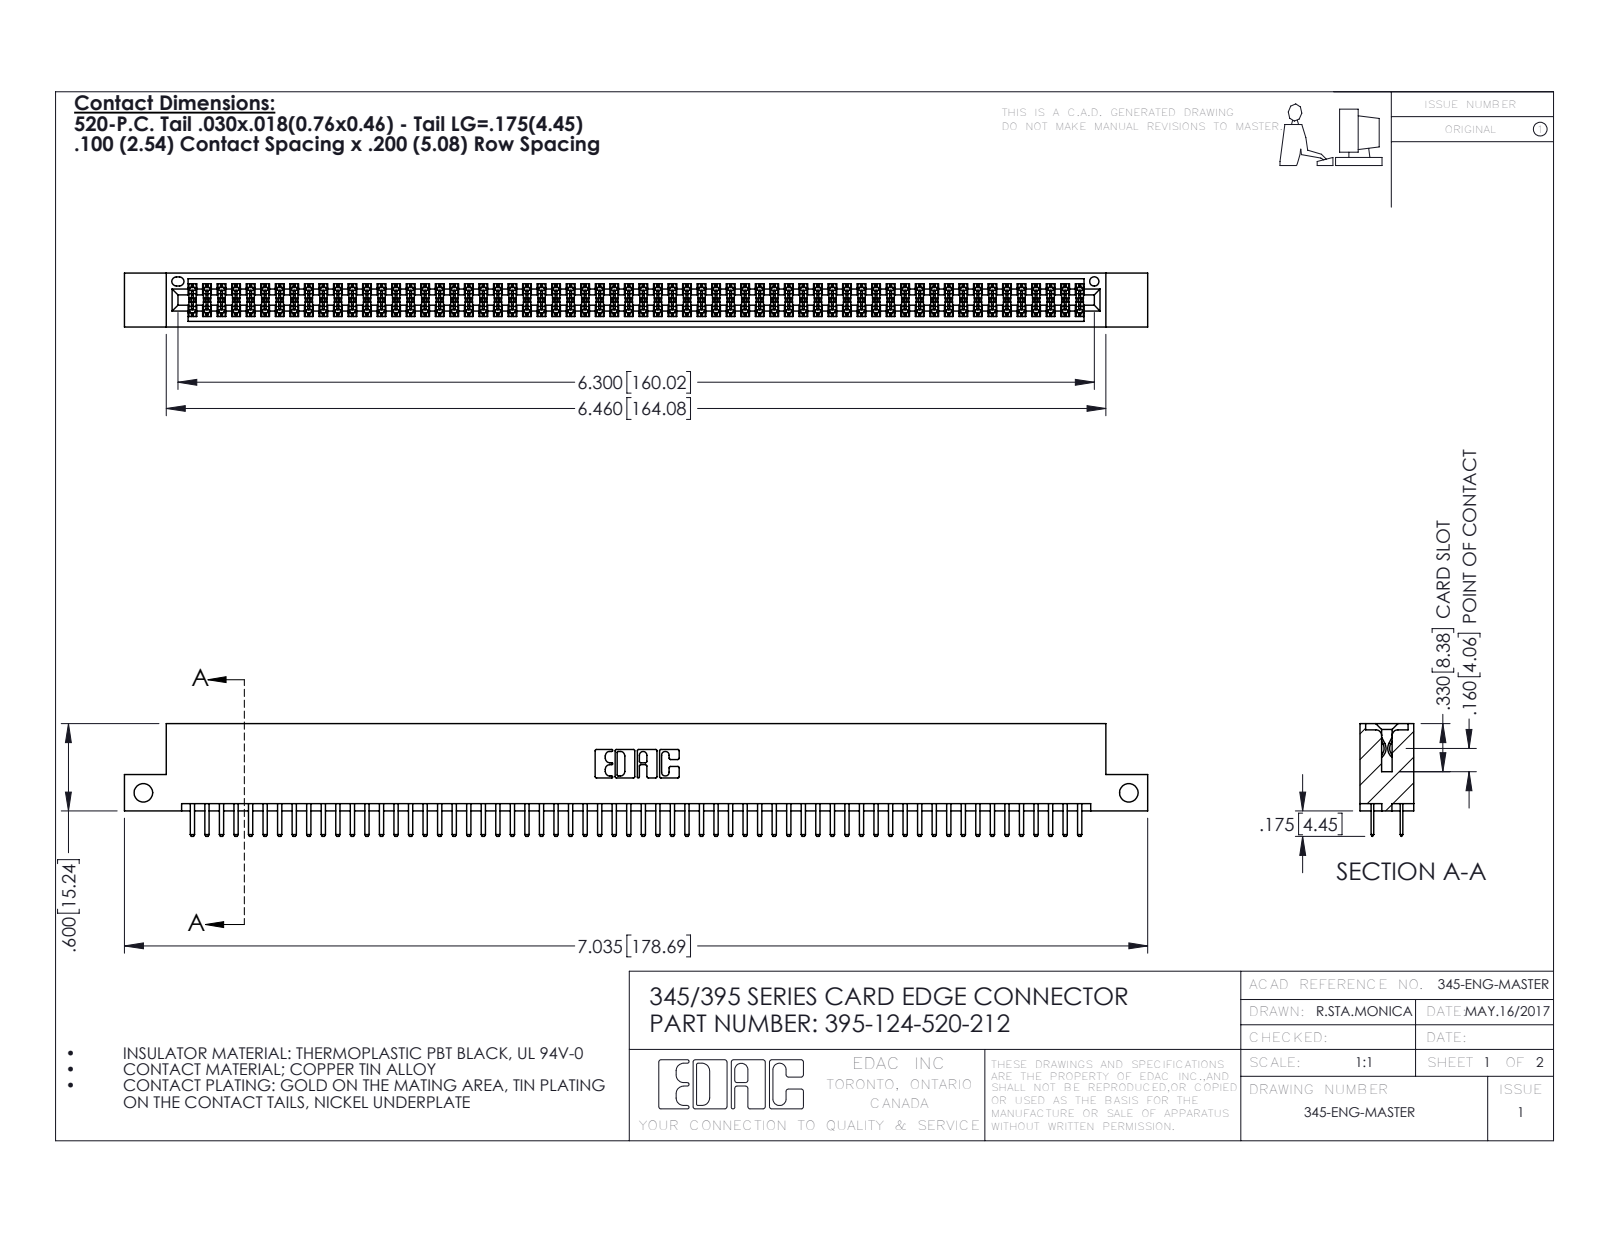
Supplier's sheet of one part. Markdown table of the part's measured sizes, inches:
| quantity | value |
| --- | --- |
| part name | 345 Part_Flush Mounting Lugs - Side Mount; 345-292-001_345-293-120; 395-124-520-212 |
| STEP written by | SolidWorks 2016 (CONFIG_CONTROL_DESIGN) |
| units | inches |
| bodies | 125 solids, 6822 faces (4420 planar, 2402 cylindrical, 0 other) |
| overall size | 7.035 × 0.775 × 0.37 |
| volume | 1.062 in³ |
| surface area | 40.08 in² |
| round holes (diameter × count) | 0.128 × 2, 0.064 × 1 |
| partial cylindrical surfaces (radius × count) | 0.006 × 186, 0.01 × 128, 0.01 × 22, 0.007 × 6, 0.031 × 6, 0.026 × 3, 0.014 × 2, 0.019 × 2 |
| main face-to-face distances | 0.298, 0.072, 0.2, 0.37, 0.098, 0.272, 0.025, 0.225, 0.022, 0.072 |
| hole center spacings | 6.775 |
